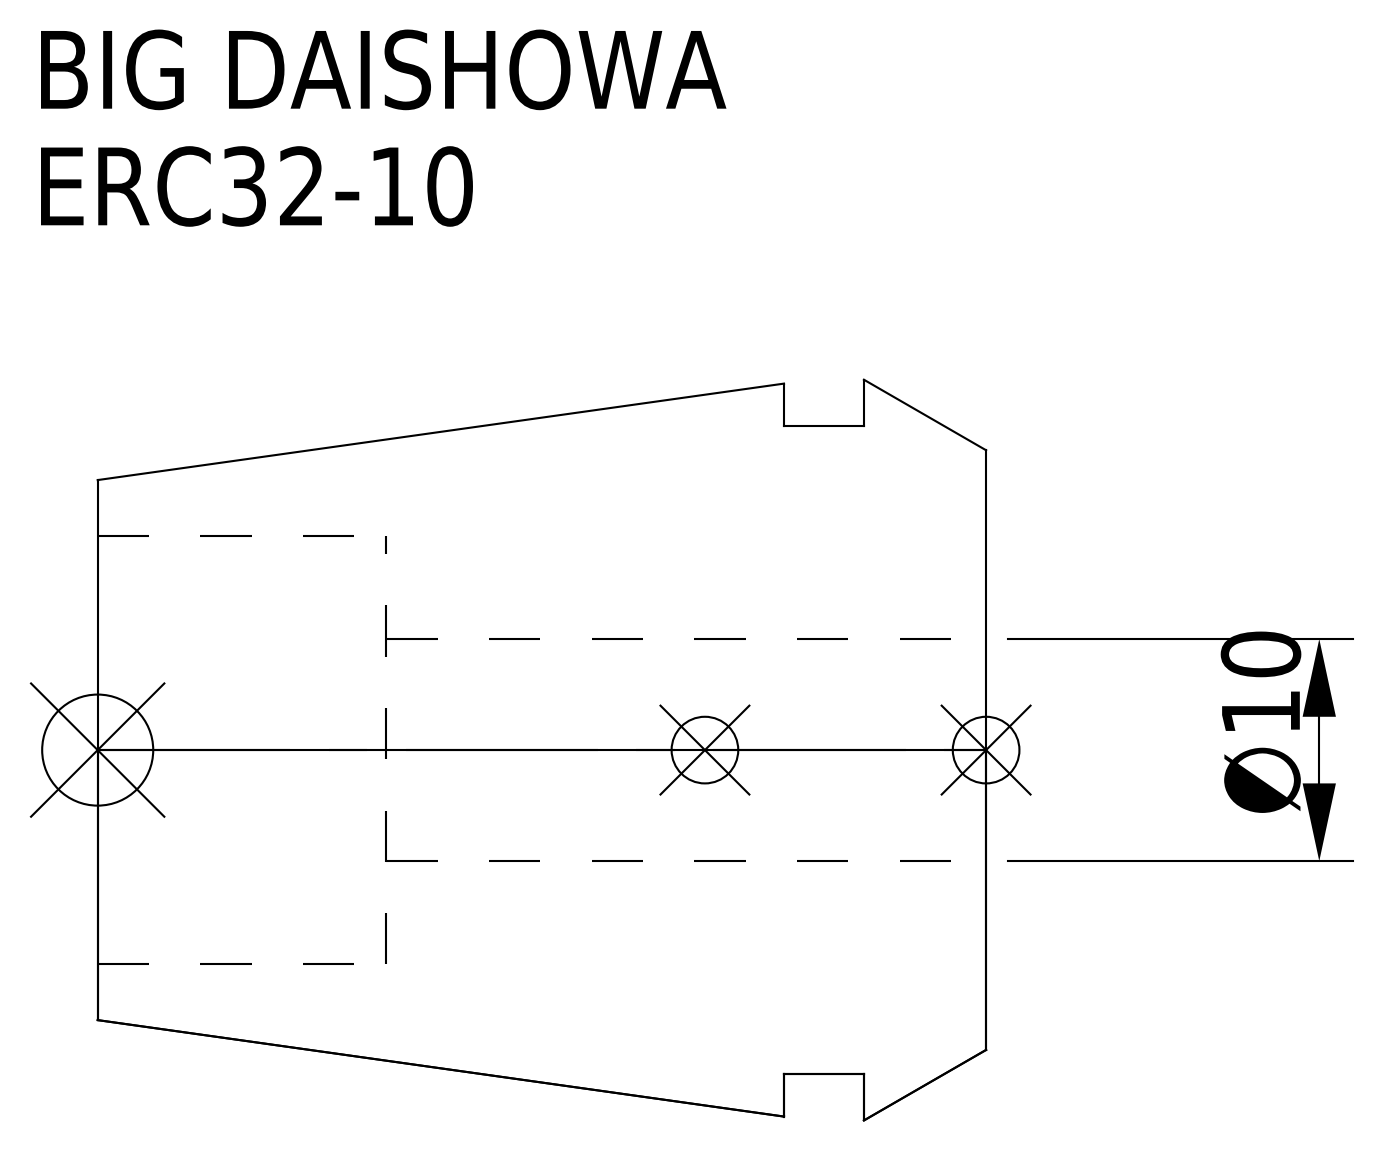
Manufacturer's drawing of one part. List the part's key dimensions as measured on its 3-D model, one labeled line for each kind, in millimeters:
Part name (STEP PRODUCT): ERC32-10
STEP written by: CREO PARAMETRIC BY PTC INC, 2016380 (AUTOMOTIVE_DESIGN)
Units: millimetres
Bodies: 1 solid, 15 faces (5 planar, 6 cylindrical, 4 other)
Overall size (bounding box): 40 × 33.35 × 33.35
Volume: 20 519 mm³ · Surface area: 6 647 mm²
Round holes (diameter × count): ⌀10 ×1, ⌀19.3 ×1
Round bosses / shafts (diameter × count): ⌀29.2 ×1
Main face-to-face distances: 27, 5.5, 21.5, 9.1, 3.6, 17.9, 40, 34.5, 30.9, 13
